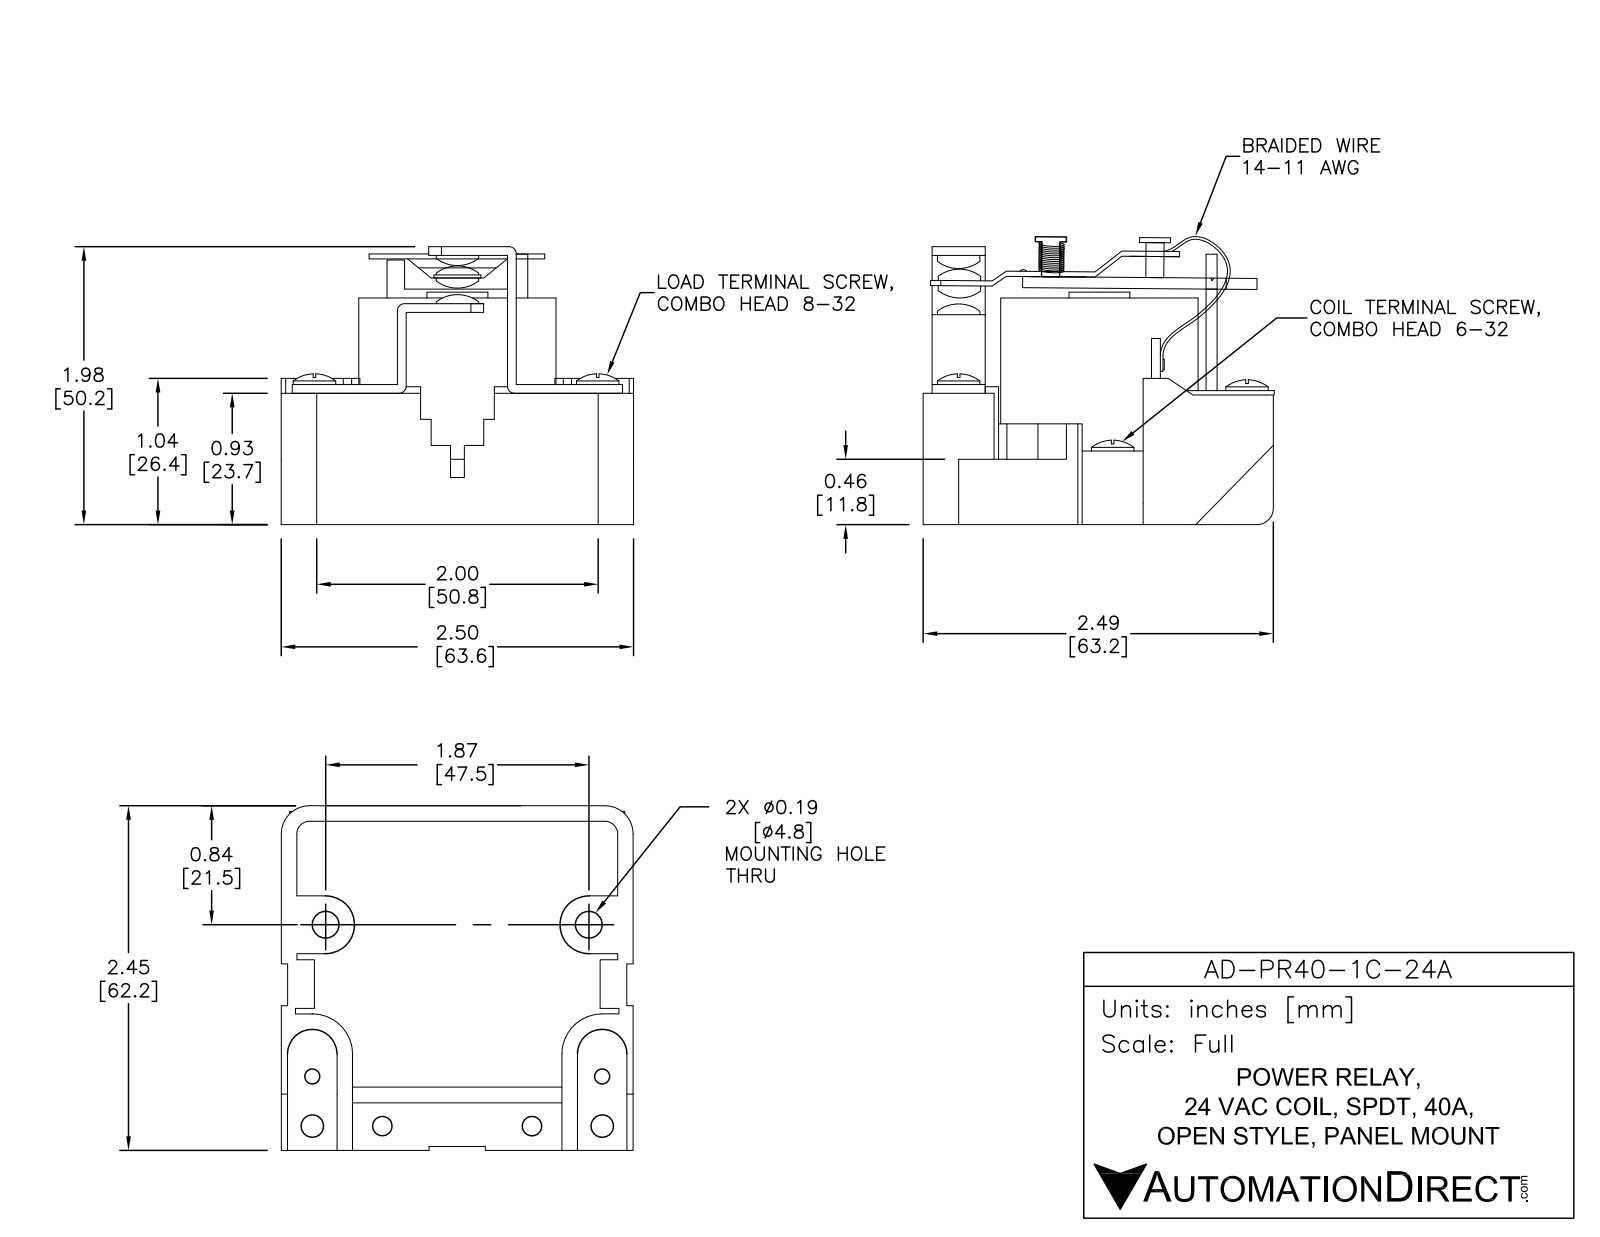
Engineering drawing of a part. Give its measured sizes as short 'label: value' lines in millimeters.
name: AD-PR40-1C-24A
written by: SolidWorks 2013 (AUTOMOTIVE_DESIGN)
unit: mm
bodies: 34 solids, 627 faces (420 planar, 128 cylindrical, 79 other)
size: 64.94 × 64.1 × 51.55
volume: 91 031 mm³; area: 33 435 mm²
holes: 4× ⌀5, 2× ⌀2.5, 2× ⌀3.33, 2× ⌀10, 1× ⌀30
bosses: 3× ⌀7.75, 2× ⌀6.85, 2× ⌀5.28, 1× ⌀35.5, 1× ⌀18, 1× ⌀10, 1× ⌀6.5, 1× ⌀5.5
rounds: 10× R0.75, 6× R3, 4× R0.38, 4× R1, 4× R1.48, 4× R1.5, 3× R2, 2× R0.5
face distances: 12, 2, 10, 64, 32.75, 1.75, 1, 1.5, 30.75, 6.5
hole spacings: 10, 26.2, 27.51, 29.92, 36.54, 37.51, 49.24, 50.25
